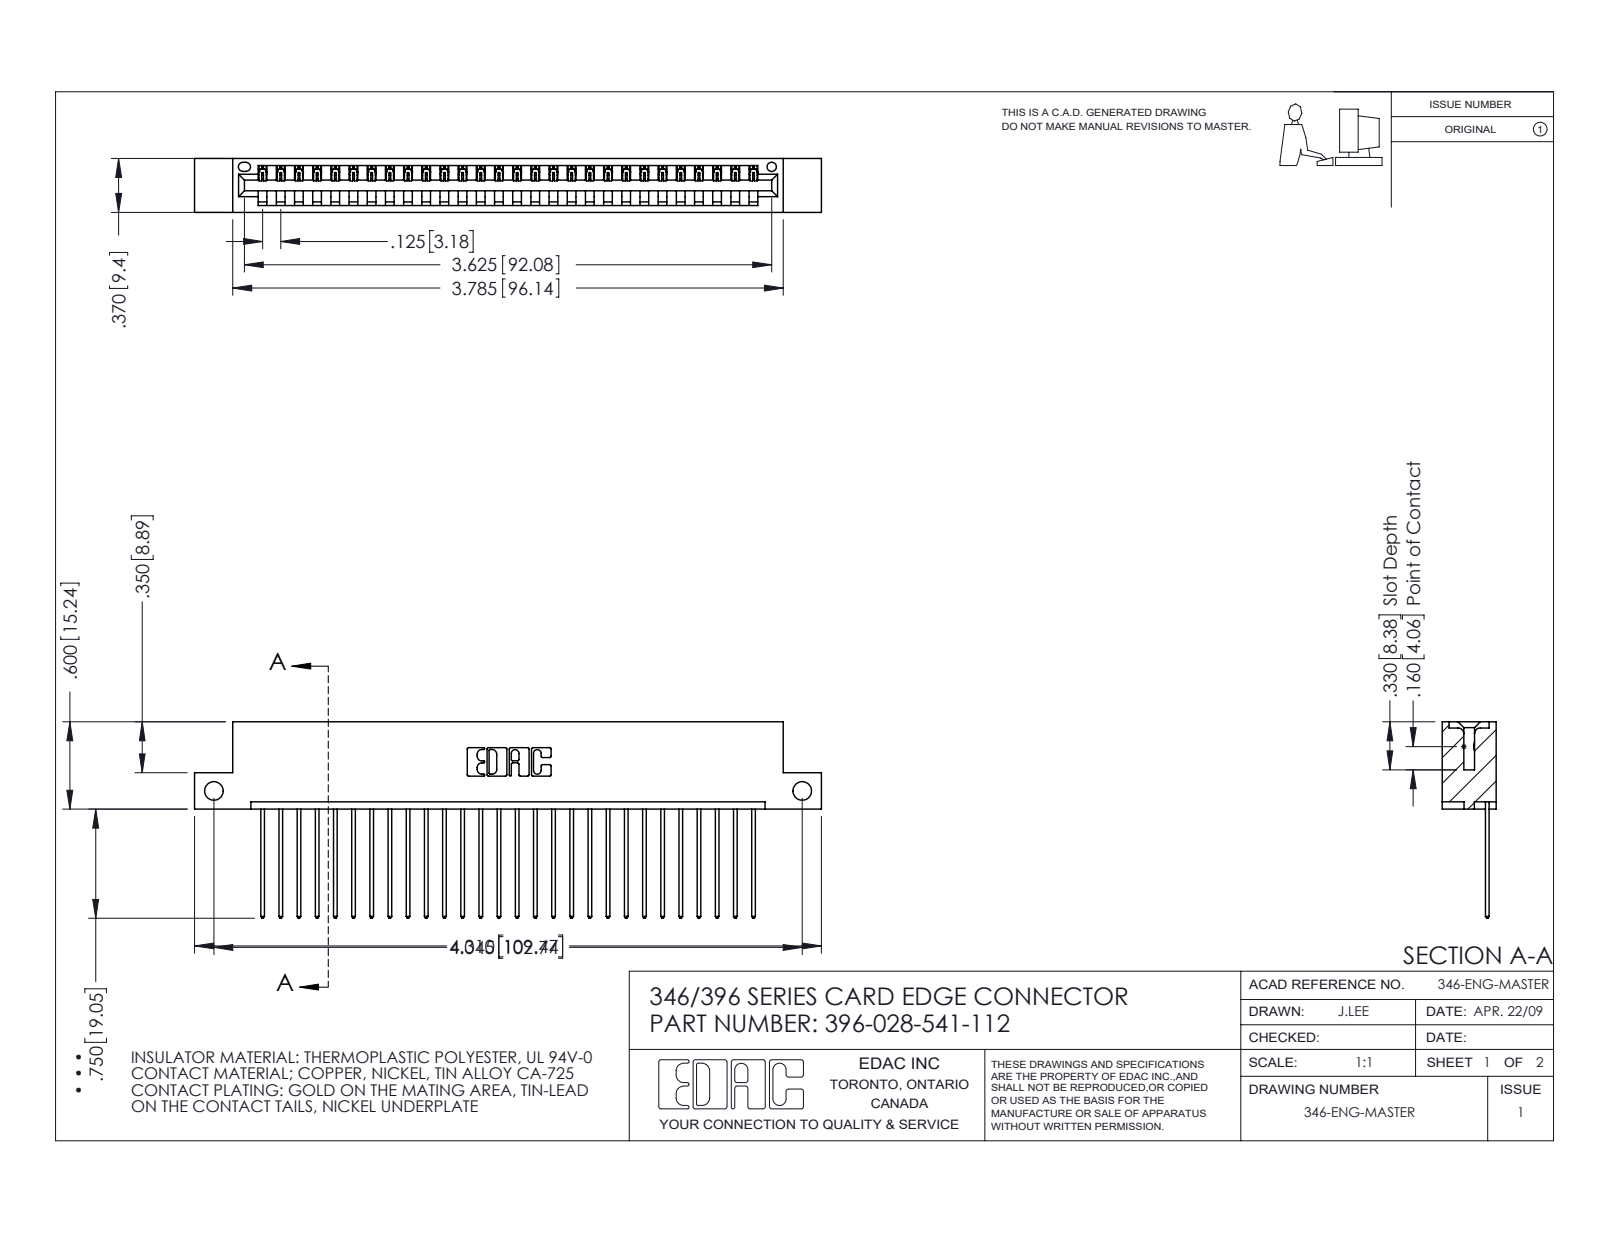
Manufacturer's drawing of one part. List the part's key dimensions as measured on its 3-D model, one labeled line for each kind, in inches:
Part name (STEP PRODUCT): 346 Part_Flush Mounting Lugs - Side Mount; 345-292-001_345-293-141; 396-028-541-112
STEP written by: SolidWorks 2016 (CONFIG_CONTROL_DESIGN)
Units: inches
Bodies: 29 solids, 1746 faces (1196 planar, 550 cylindrical, 0 other)
Overall size (bounding box): 4.31 × 1.35 × 0.37
Volume: 0.634 in³ · Surface area: 20.52 in²
Round holes (diameter × count): ⌀0.128 ×2, ⌀0.064 ×1
Partial cylindrical surfaces — rounded edges, fillets, slot ends (radius × count): R0.006 ×56, R0.01 ×56, R0.01 ×22, R0.007 ×6, R0.031 ×6, R0.026 ×3, R0.031 ×2, R0.04 ×2
Main face-to-face distances: 0.048, 0.322, 0.25, 0.37, 0.072, 0.298, 0.025, 0.148, 0.222, 0.1
Hole centre spacings: 4.045
